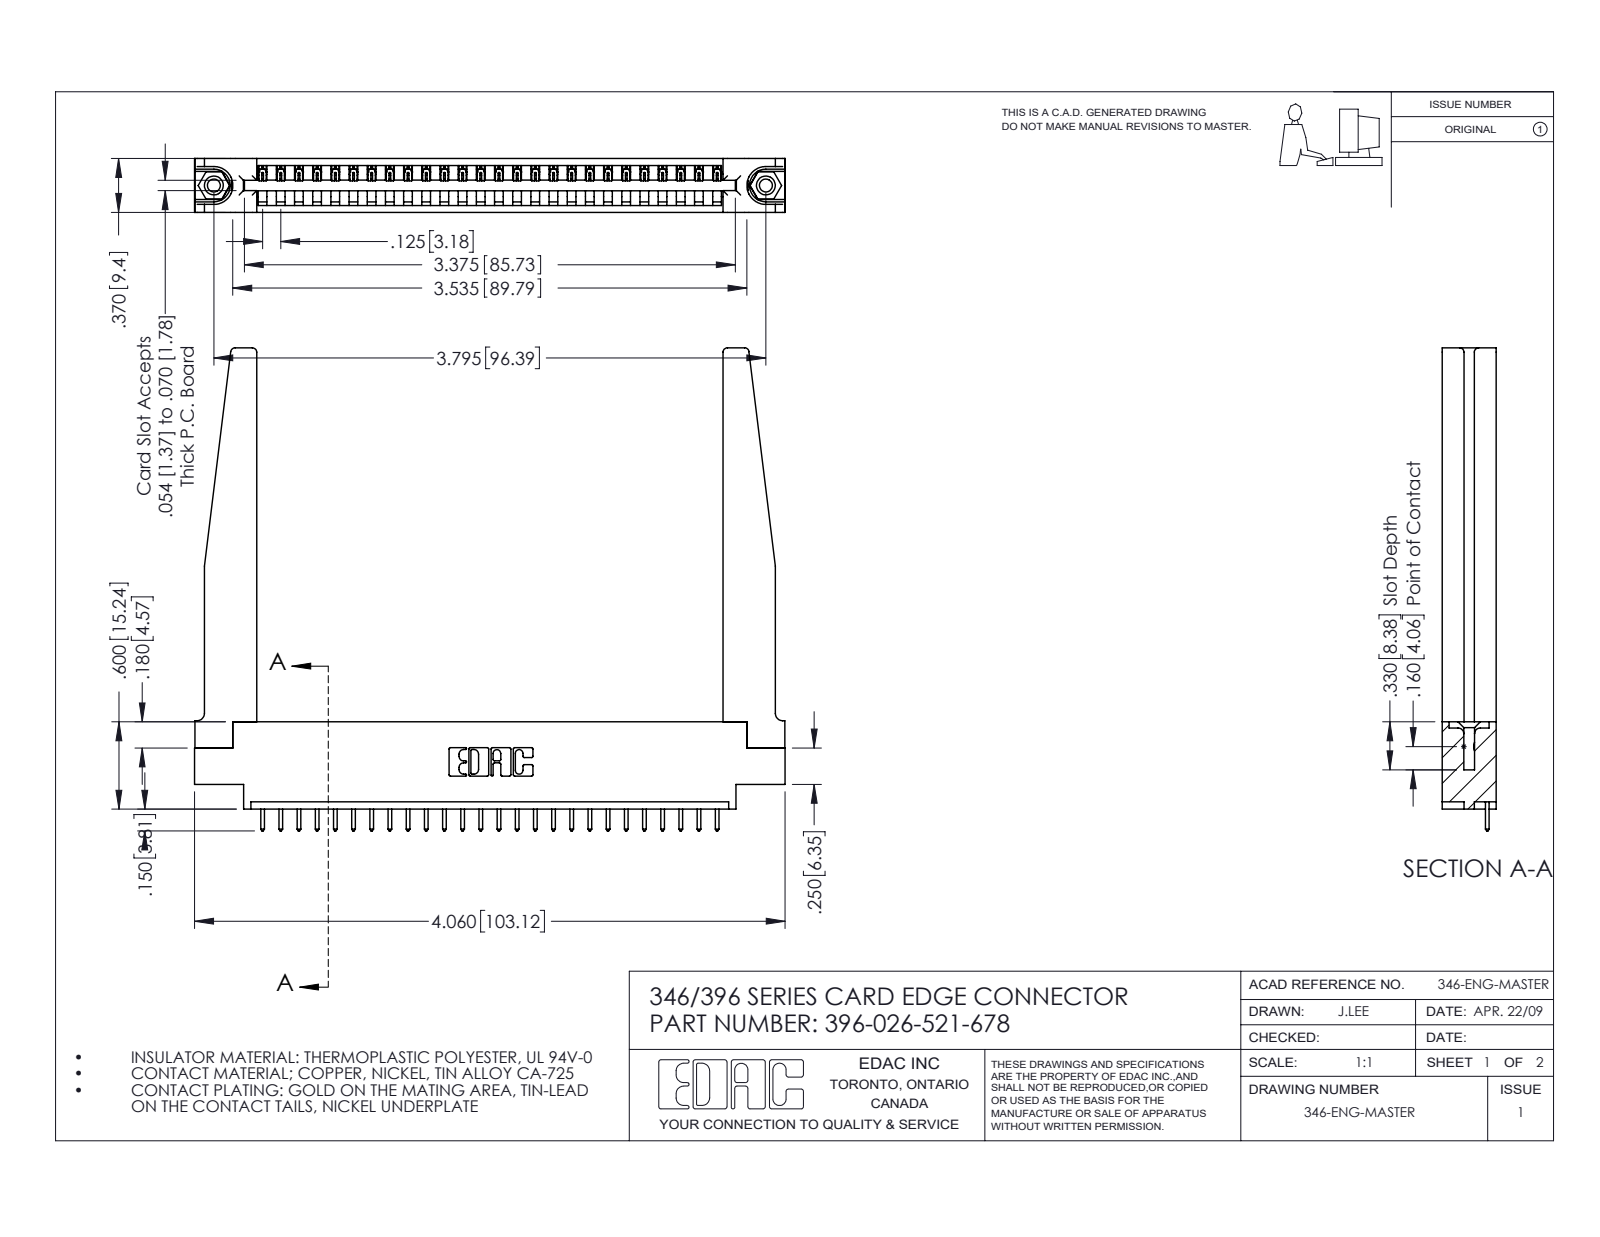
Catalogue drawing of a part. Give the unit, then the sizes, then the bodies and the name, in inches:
Units: inches
Overall size (bounding box): 4.06 × 3.32 × 0.37
Round holes (diameter × count): ⌀0.089 ×2, ⌀0.125 ×2, ⌀0.156 ×2, ⌀0.064 ×1
Round bosses / shafts (diameter × count): ⌀0.155 ×2
Partial cylindrical surfaces — rounded edges, fillets, slot ends (radius × count): R0.006 ×52, R0.01 ×52, R0.01 ×22, R0.03 ×8, R0.007 ×6, R0.031 ×6, R0.026 ×3, R0.031 ×2
Main face-to-face distances: 0.37, 0.048, 0.322, 0.072, 0.148, 0.15, 0.25, 0.298, 0.025, 0.222
Hole centre spacings: 0.246, 3.587, 3.795
Volume: 1.003 in³ · Surface area: 28.13 in²
Bodies: 31 solids, 1868 faces (1262 planar, 554 cylindrical, 52 other)
Part name (STEP PRODUCT): 346-220-078_345-220-078; 345-292-001_345-293-121; 346 Part_0.170 Offset - 0.156 Dia-TH; 396-026-521-678 (+1 more)
STEP written by: SolidWorks 2016 (CONFIG_CONTROL_DESIGN)
